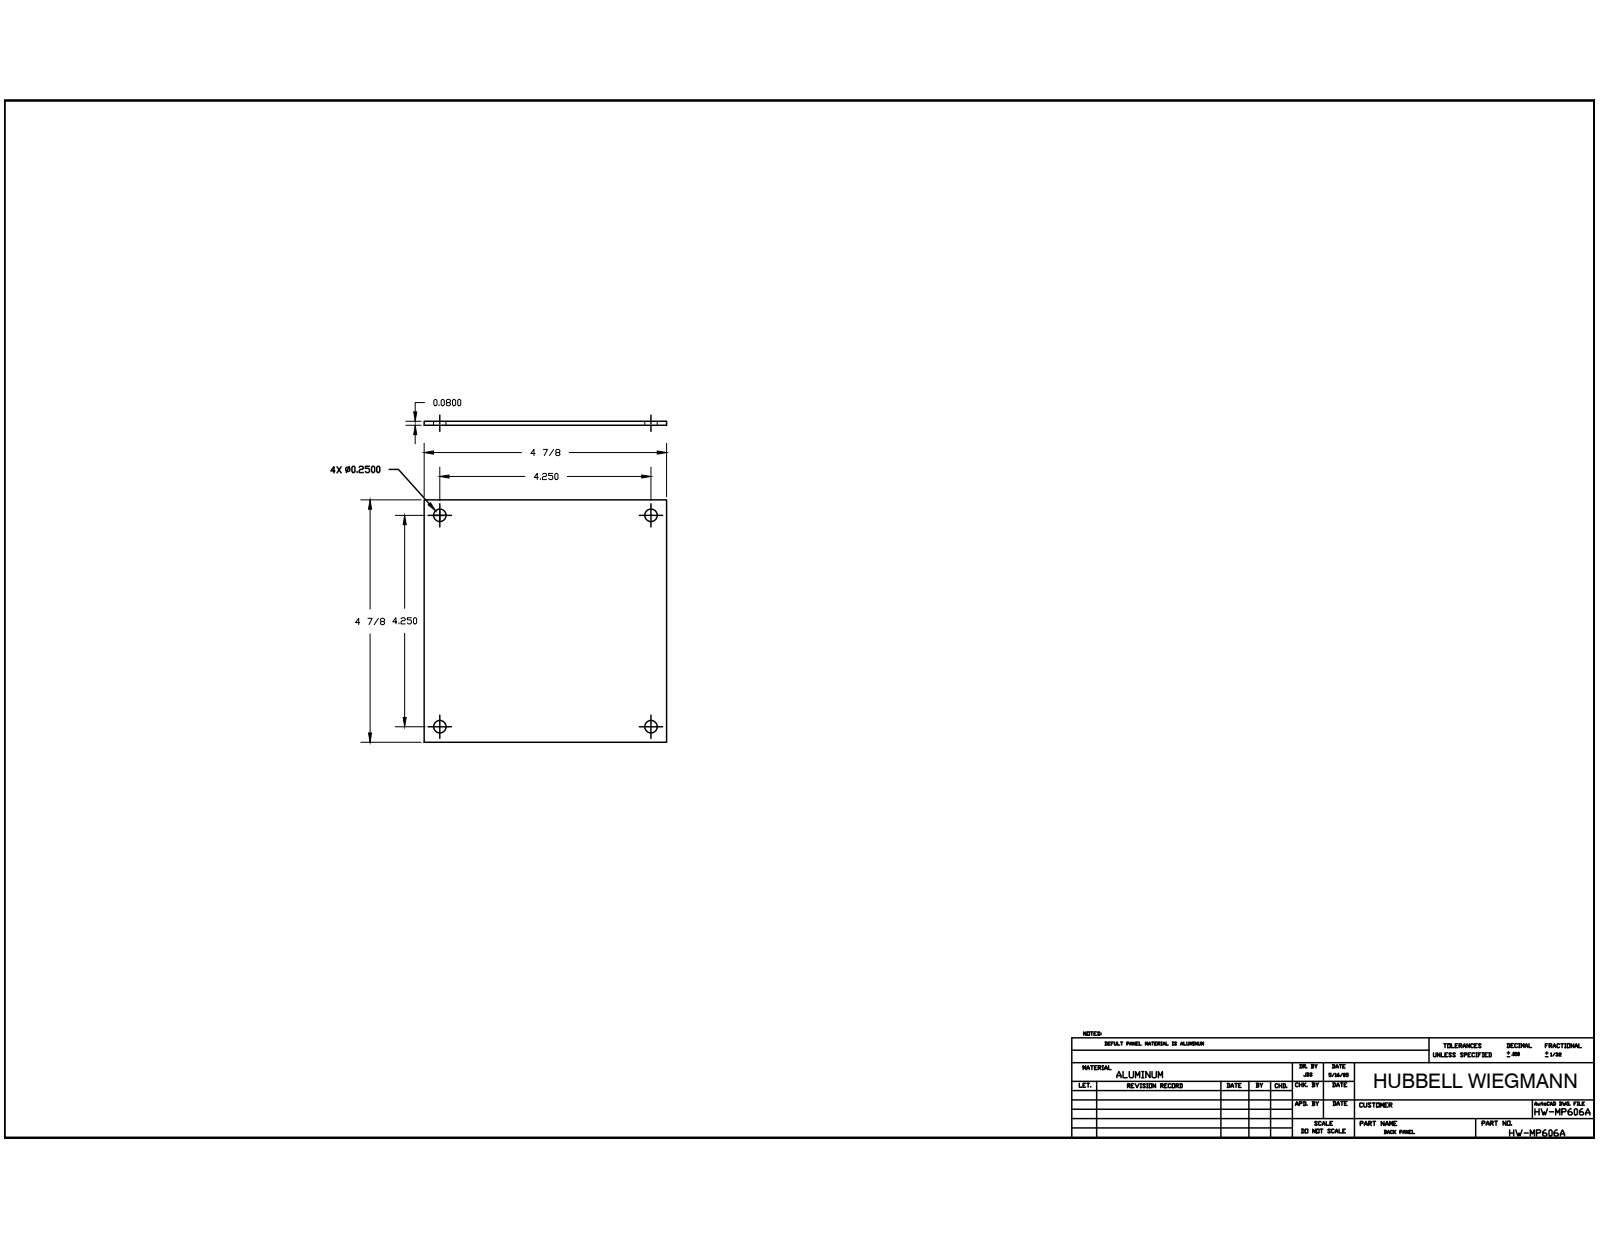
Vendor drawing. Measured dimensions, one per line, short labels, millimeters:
name: BP66AL_STP
written by: Autodesk Inventor 2014 (AUTOMOTIVE_DESIGN)
unit: mm
bodies: 1 solid, 10 faces (6 planar, 4 cylindrical, 0 other)
size: 123.83 × 123.83 × 2.03
volume: 30 898 mm³; area: 31 580 mm²
holes: 4× ⌀6.35
face distances: 2.03, 123.82
hole spacings: 107.94, 152.65
